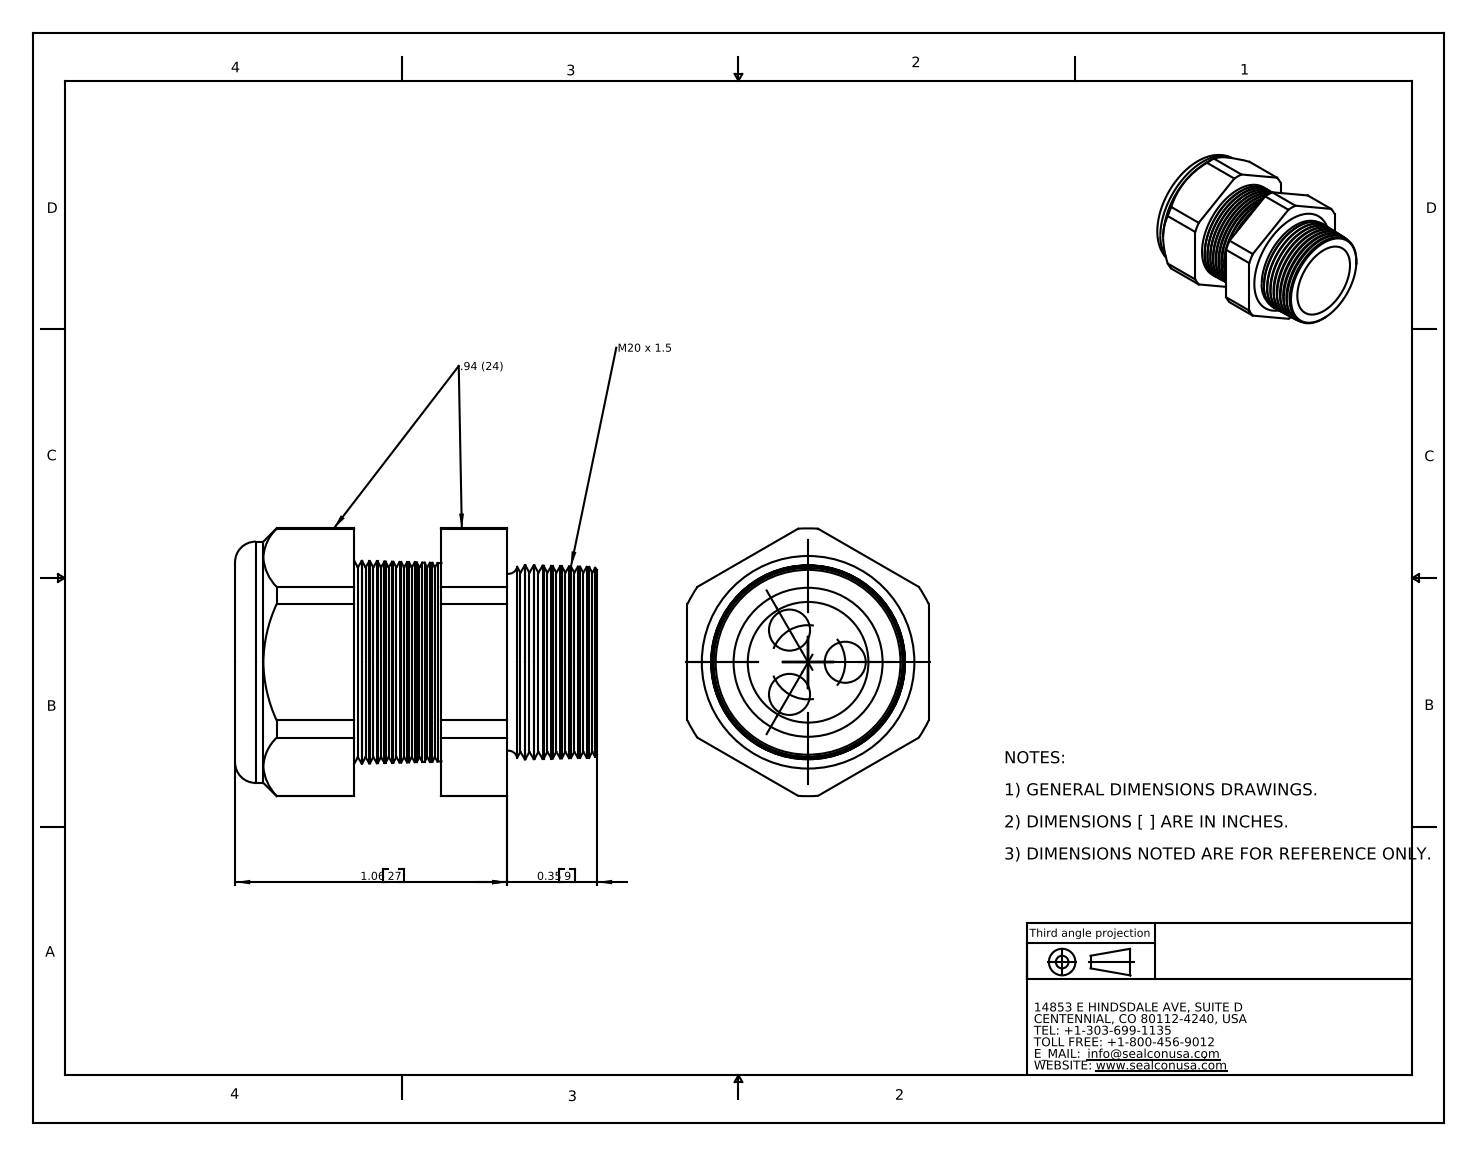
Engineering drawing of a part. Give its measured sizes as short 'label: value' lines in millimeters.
name: CD20M3-GY
written by: SolidWorks 2007 (CONFIG_CONTROL_DESIGN)
unit: mm
bodies: 2 solids, 180 faces (20 planar, 26 cylindrical, 134 other)
size: 35.8 × 26.5 × 23.9
volume: 9 370 mm³; area: 6 430 mm²
holes: 3× ⌀4.1, 1× ⌀11.4, 1× ⌀11.9
bosses: 1× ⌀23.9
rounds: 1× R13.3
face distances: 23.9, 20.4, 11.8, 8.6, 26.9, 15.1, 6.5, 35.8, 24, 15.4
hole spacings: 3.7, 6.4
